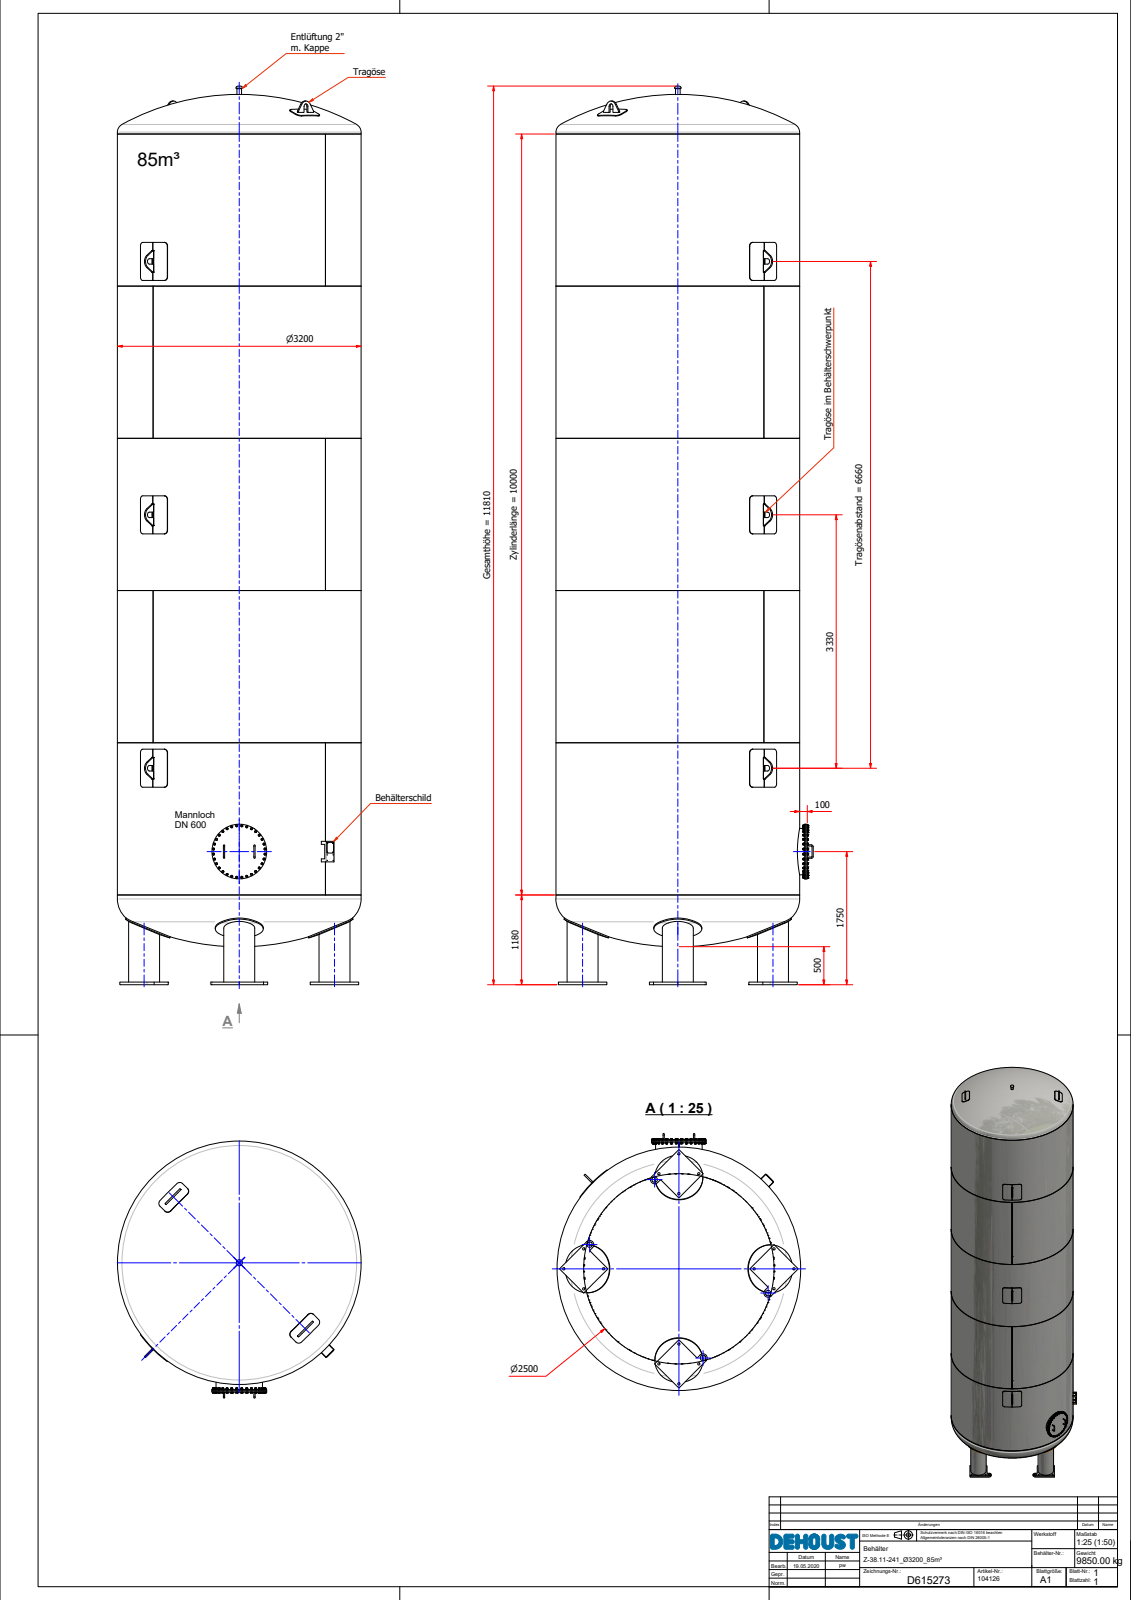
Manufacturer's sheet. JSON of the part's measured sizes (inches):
{"part_name": "D615273-0_-Behälter_Shrinkwrap_1", "step_written_by": "Autodesk Inventor 2019 (AUTOMOTIVE_DESIGN)", "units": "inches", "bodies": {"solids": 138, "faces": 1600, "planar": 821, "cylindrical": 353, "other": 426}, "overall_size": [464.979, 132.992, 125.984], "volume_in3": 68710, "surface_area_in2": 398400, "round_holes": [[0.545, 32], [0.669, 32], [0.709, 32], [1.181, 16], [0.197, 8], [0.256, 4], [2.756, 4], [9.843, 4], [15.134, 4], [2.146, 1], [2.374, 1], [3.083, 1]], "round_bosses_or_shafts": [[0.63, 38], [1.181, 32], [0.885, 32], [24.803, 4], [16, 4], [125.984, 1], [28.346, 1], [25.984, 1]], "partial_cylinders_radius": [[2.205, 8], [1.417, 5], [3.74, 5], [0.394, 4], [2.165, 4], [0.079, 2], [0.276, 2], [49.213, 1]], "face_to_face_distances": [1.378, 78.74, 157.48, 0.63, 236.22, 314.961, 0.748, 46.464, 45.086, 0.118], "hole_center_spacings": [18.93, 24.733, 26.643, 2.624, 23.61, 7.771, 22.259, 10.245]}
